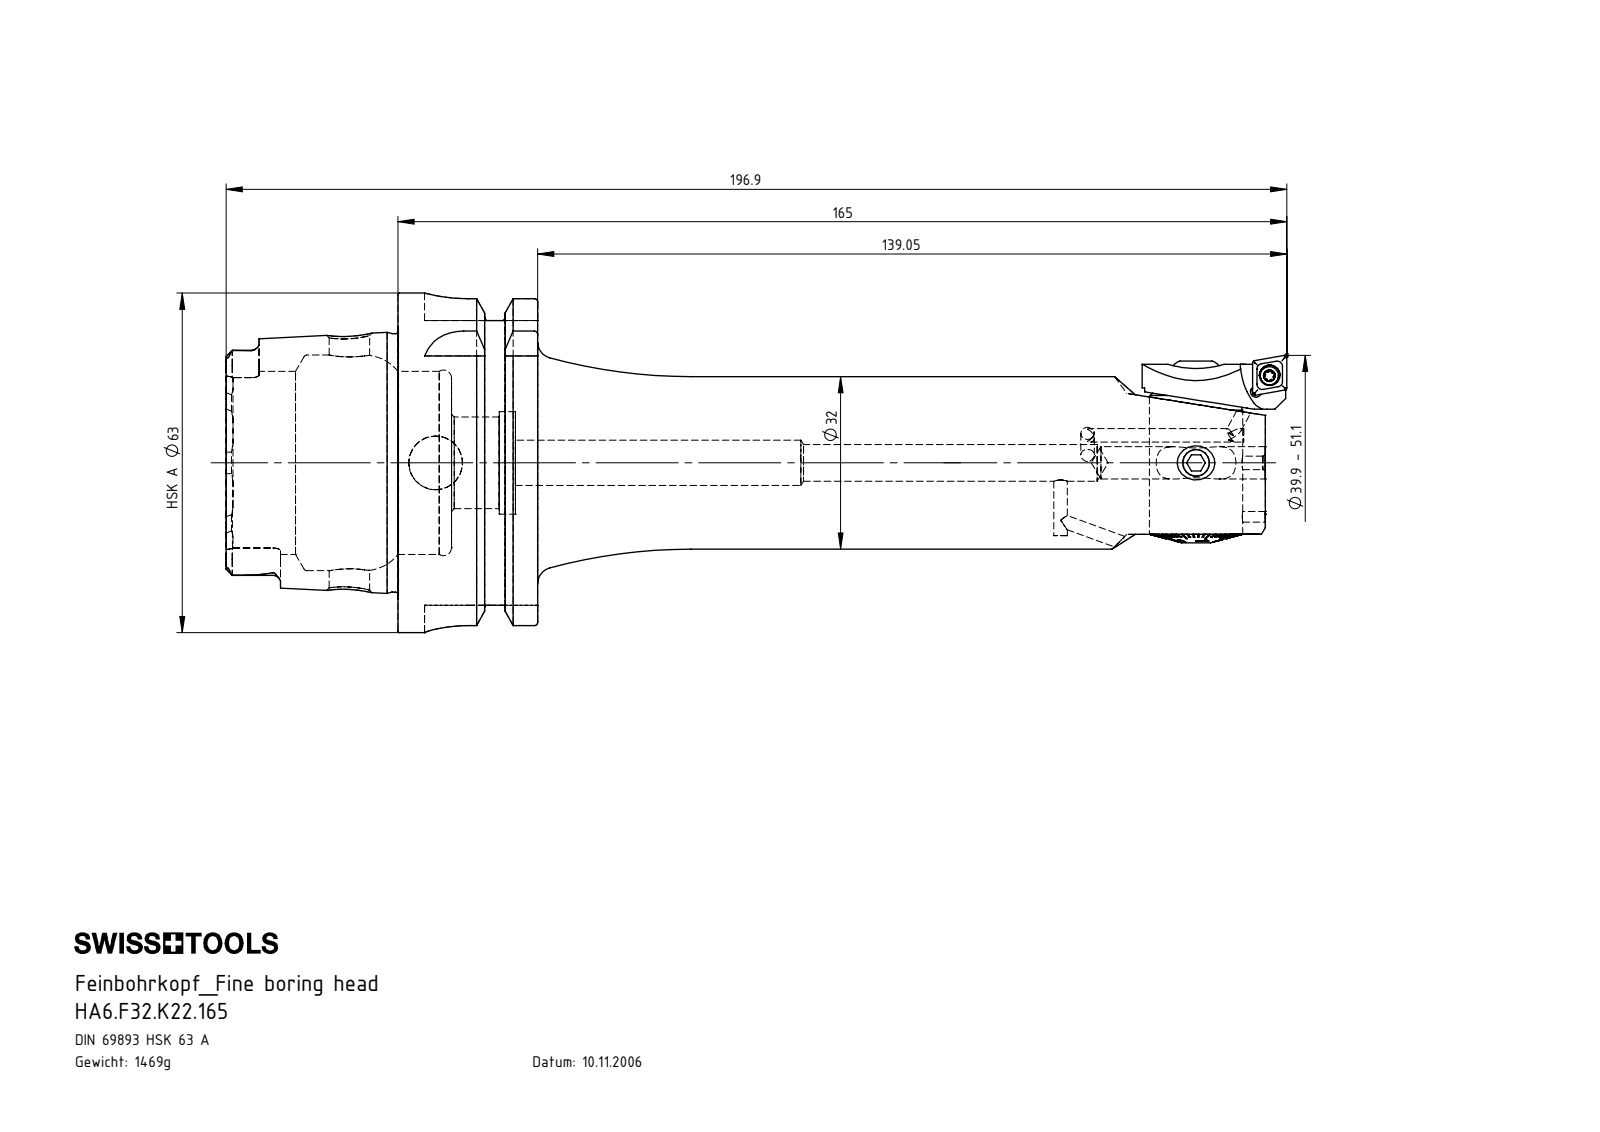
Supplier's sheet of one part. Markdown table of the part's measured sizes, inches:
| quantity | value |
| --- | --- |
| part name | CCMT060204; F32-BG2.014.012_A; F32-WCA.001.007; HA6.F32.K22.165 (+8 more) |
| STEP written by | SolidWorks 2022 (CONFIG_CONTROL_DESIGN) |
| units | inches |
| bodies | 12 solids, 853 faces (342 planar, 175 cylindrical, 336 other) |
| overall size | 7.752 × 2.48 × 2.48 |
| volume | 11.39 in³ |
| surface area | 71.84 in² |
| round holes (diameter × count) | 0.098 × 5, 0.197 × 2, 0.669 × 2, 0.079 × 1, 0.081 × 1, 0.083 × 1, 0.106 × 1, 0.11 × 1, 0.114 × 1, 0.118 × 1, 0.152 × 1, 0.236 × 1 |
| round bosses / shafts (diameter × count) | 0.394 × 2, 2.48 × 1, 2.163 × 1, 1.887 × 1, 1.26 × 1, 0.669 × 1, 0.669 × 1, 0.663 × 1 |
| partial cylindrical surfaces (radius × count) | 0.008 × 6, 0.055 × 6, 0.014 × 4, 0.02 × 4, 0.113 × 4, 0.315 × 4, 0.014 × 2, 0.069 × 2 |
| main face-to-face distances | 1.022, 0.63, 0.392, 5.947, 6.339, 5.317, 1.256, 1.648, 2.278, 7.594 |
| hole center spacings | 0.151, 0.157, 0.22, 0.224, 0.315, 0.388, 0.418, 0.46 |
